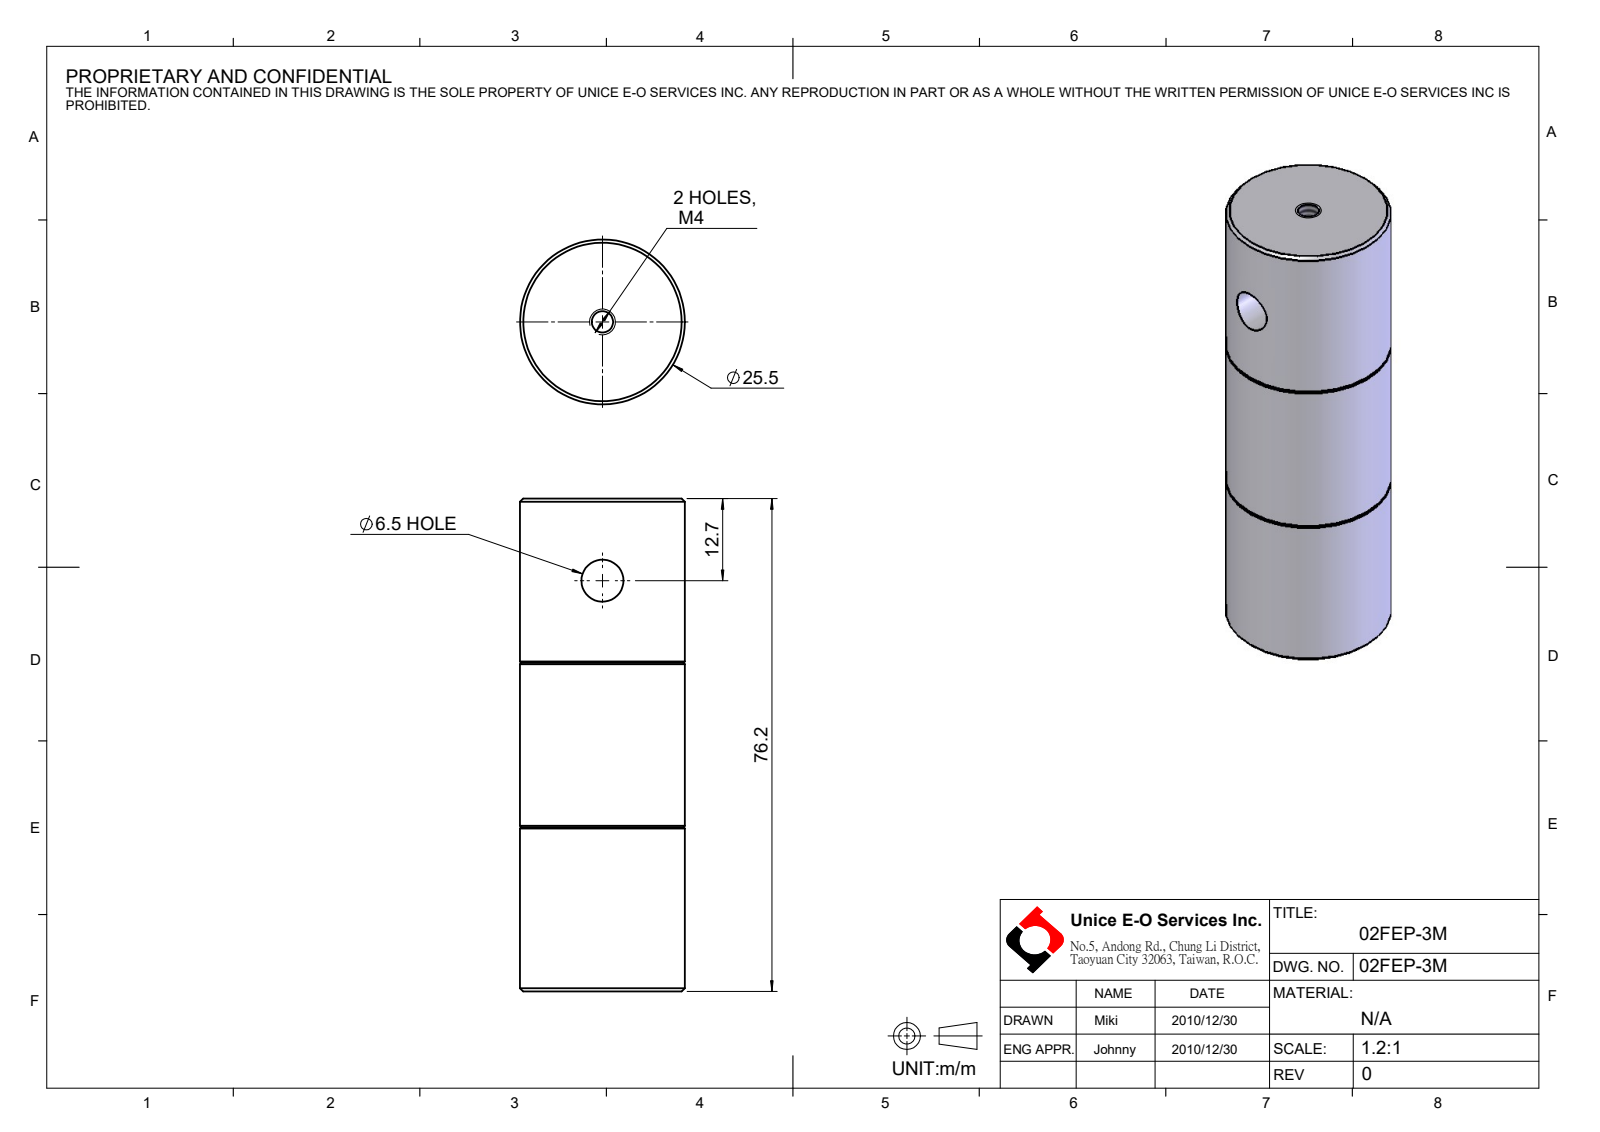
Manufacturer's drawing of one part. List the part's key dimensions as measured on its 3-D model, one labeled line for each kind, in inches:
Part name (STEP PRODUCT): 02FEP-3M
STEP written by: SolidWorks 2016 (CONFIG_CONTROL_DESIGN)
Units: inches
Bodies: 1 solid, 30 faces (2 planar, 12 cylindrical, 16 other)
Overall size (bounding box): 3 × 1.004 × 1.004
Volume: 2.313 in³ · Surface area: 11.96 in²
Round holes (diameter × count): ⌀0.13 ×1, ⌀0.256 ×1
Round bosses / shafts (diameter × count): ⌀1.004 ×1
Main face-to-face distances: 3
